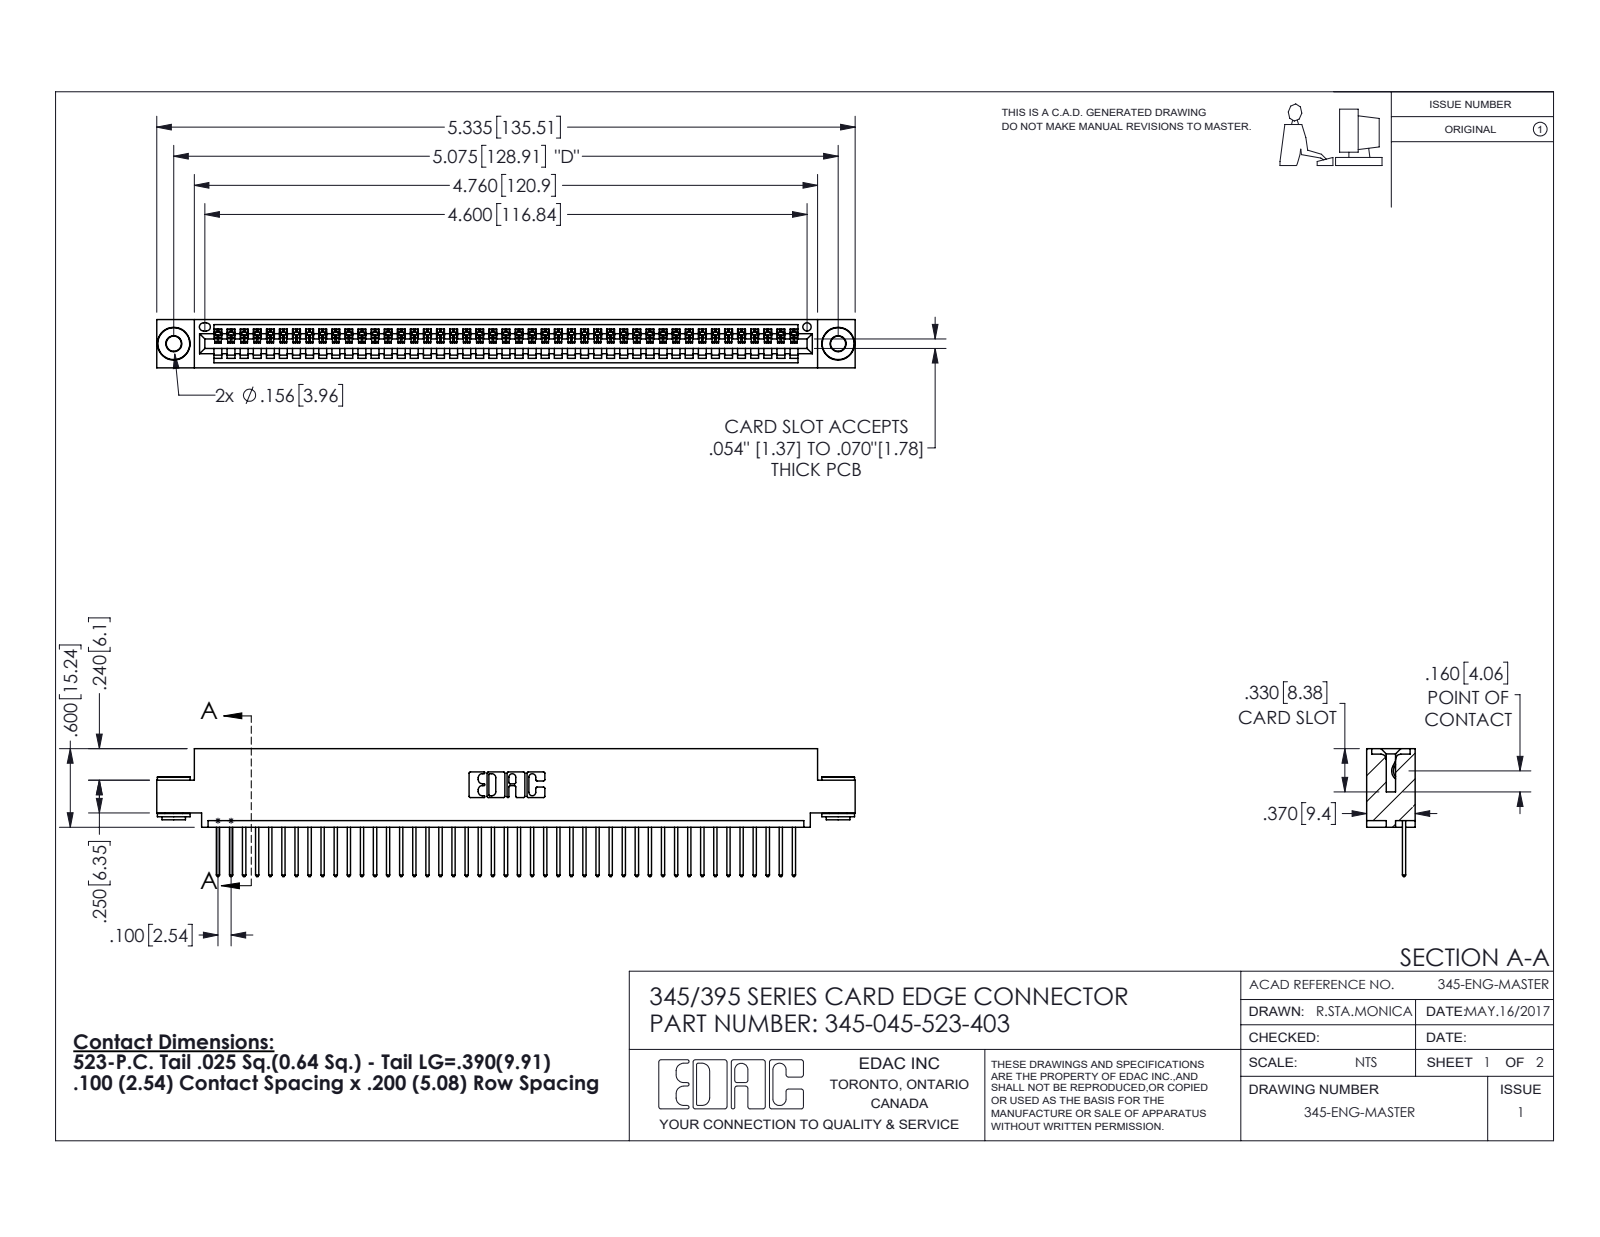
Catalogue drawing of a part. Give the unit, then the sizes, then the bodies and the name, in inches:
Units: inches
Overall size (bounding box): 5.335 × 0.977 × 0.37
Round holes (diameter × count): ⌀0.116 ×2, ⌀0.156 ×2, ⌀0.064 ×1
Round bosses / shafts (diameter × count): ⌀0.25 ×2, ⌀0.18 ×2, ⌀0.136 ×2
Partial cylindrical surfaces — rounded edges, fillets, slot ends (radius × count): R0.006 ×90, R0.01 ×90, R0.01 ×22, R0.007 ×6, R0.031 ×6, R0.026 ×3, R0.031 ×2, R0.04 ×2
Main face-to-face distances: 0.072, 0.298, 0.37, 0.025, 0.2, 0.098, 0.272, 0.225, 0.149, 0.072
Hole centre spacings: 0.27, 4.839, 5.075
Volume: 0.783 in³ · Surface area: 27.01 in²
Bodies: 48 solids, 2778 faces (1894 planar, 876 cylindrical, 8 other)
Part name (STEP PRODUCT): 345-250-002_345-250-002-102; 345-292-001_345-293-123; 345-045-523-403; 345 Part_0.110 Offset - 0.156 Dia-TH
STEP written by: SolidWorks 2016 (CONFIG_CONTROL_DESIGN)
